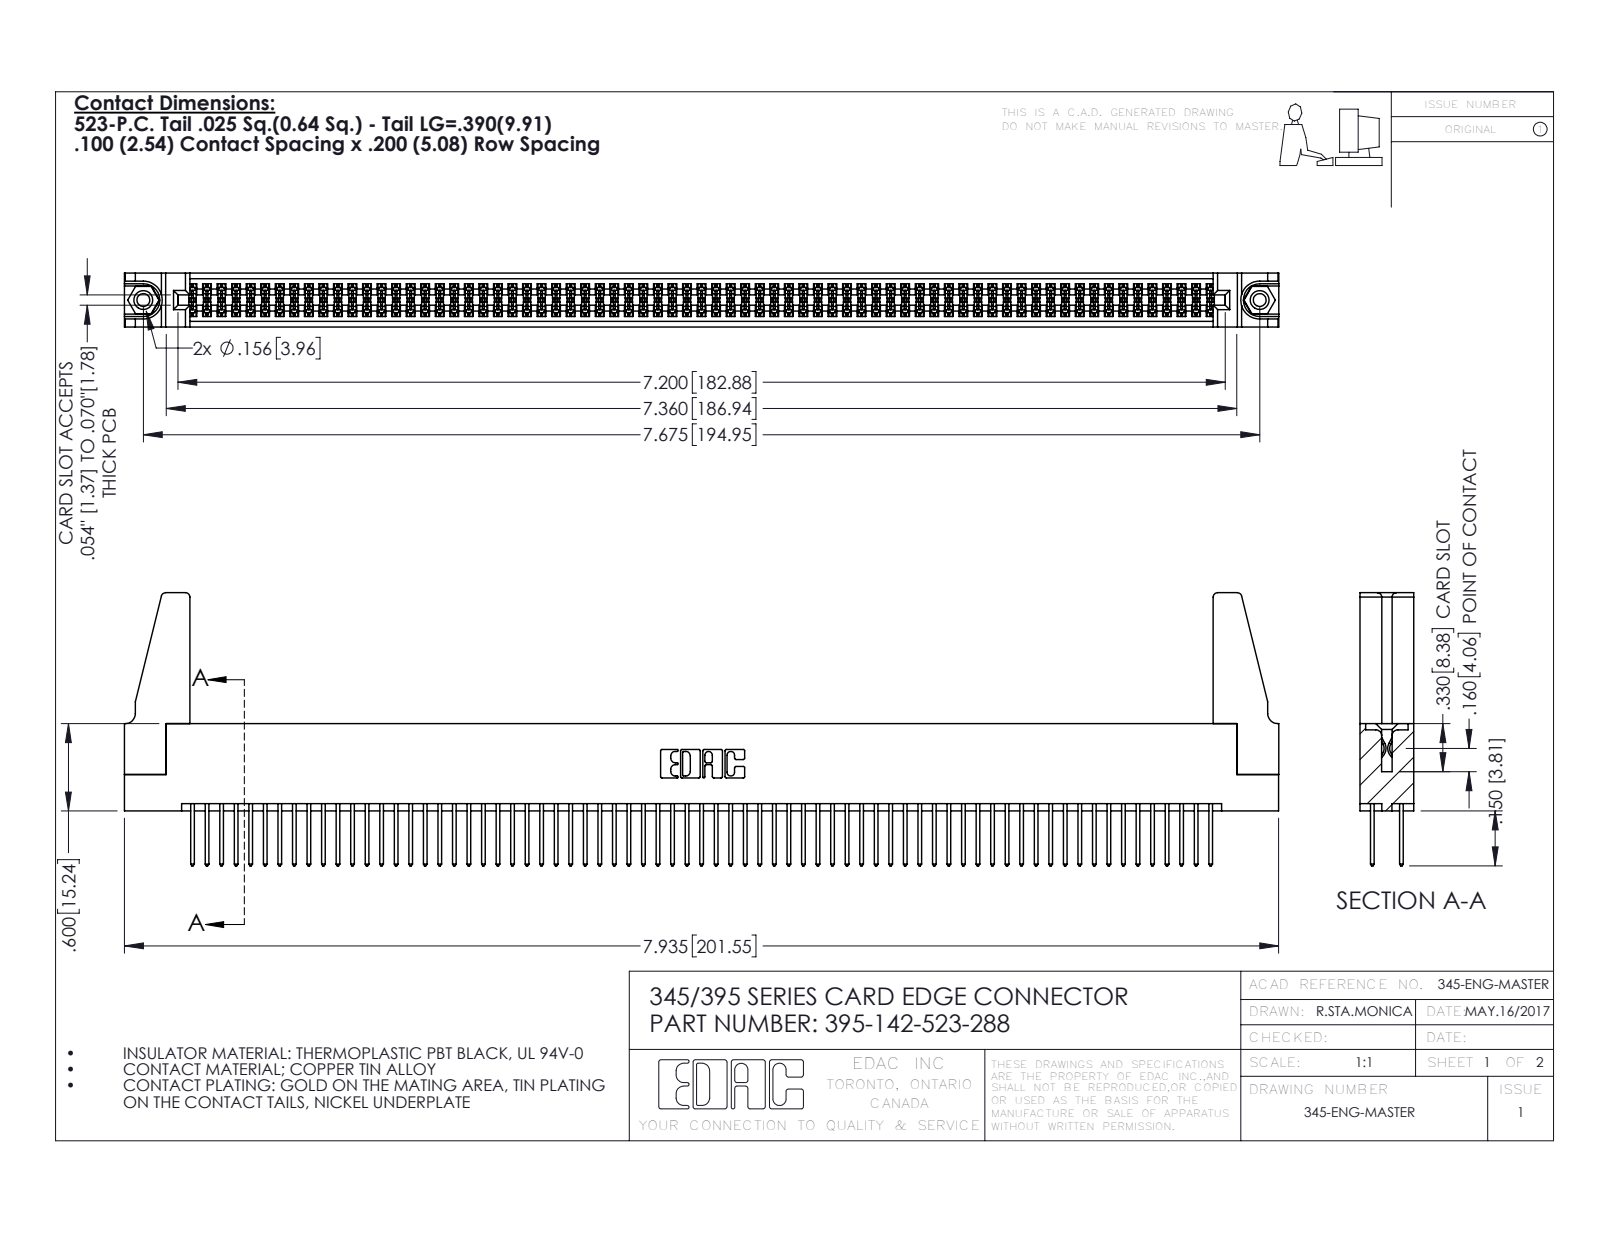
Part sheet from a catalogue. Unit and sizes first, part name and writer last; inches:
Units: inches
Overall size (bounding box): 7.936 × 1.877 × 0.37
Round holes (diameter × count): ⌀0.089 ×2, ⌀0.125 ×2, ⌀0.156 ×2, ⌀0.064 ×1
Round bosses / shafts (diameter × count): ⌀0.155 ×2
Partial cylindrical surfaces — rounded edges, fillets, slot ends (radius × count): R0.006 ×213, R0.01 ×142, R0.01 ×22, R0.03 ×8, R0.007 ×6, R0.031 ×6, R0.026 ×3, R0.014 ×2
Main face-to-face distances: 0.072, 0.298, 0.2, 0.098, 0.272, 0.025, 0.37, 0.225, 0.175, 0.149
Hole centre spacings: 0.27, 7.439, 7.675
Volume: 1.428 in³ · Surface area: 53.88 in²
Bodies: 147 solids, 7350 faces (4838 planar, 2496 cylindrical, 16 other)
Part name (STEP PRODUCT): 345-220-078_345-220-088; 345-292-001_345-293-123; 395-142-523-288; 345-250-001_345-250-001-102 (+1 more)
STEP written by: SolidWorks 2016 (CONFIG_CONTROL_DESIGN)
